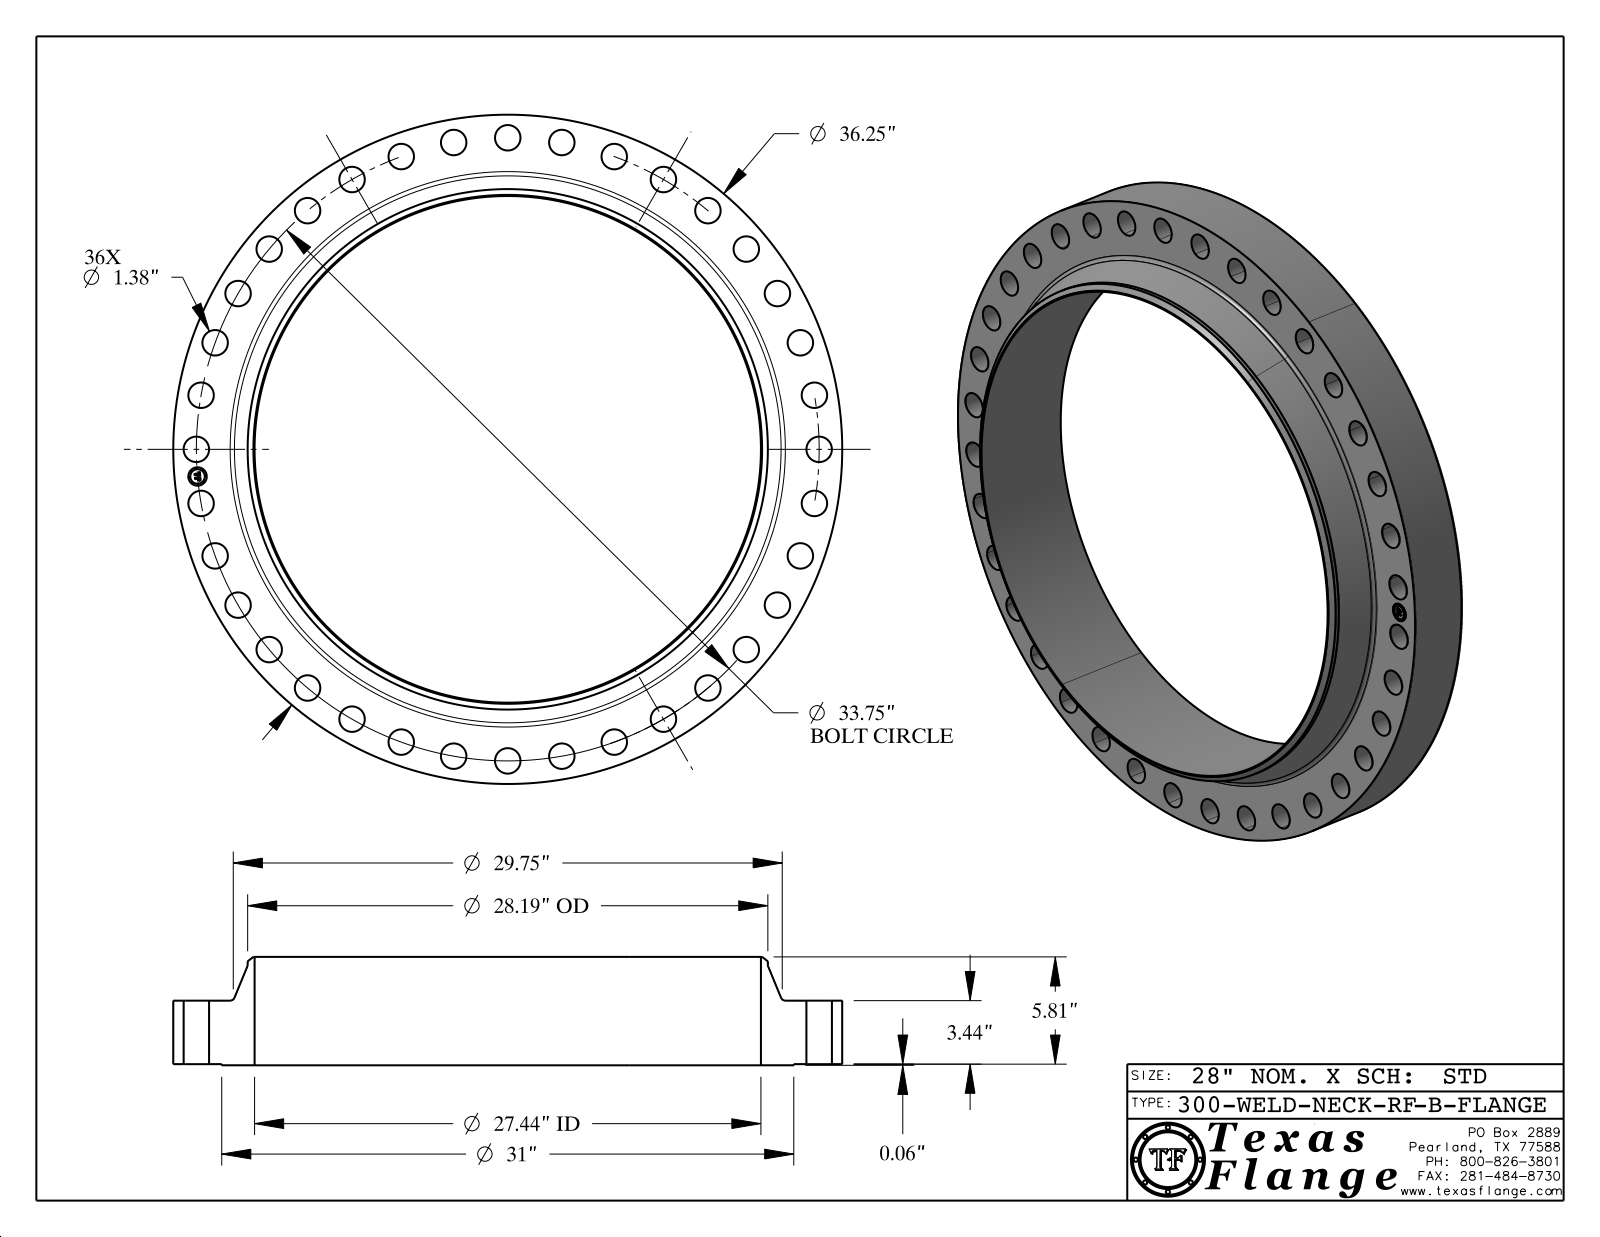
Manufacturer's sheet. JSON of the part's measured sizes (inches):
{"part_name": "300-WELD-NECK-RF, Series B", "step_written_by": "CATIA V5 STEP AP214 (AUTOMOTIVE_DESIGN)", "units": "inches", "bodies": {"solids": 1, "faces": 475, "planar": 369, "cylindrical": 100, "other": 6}, "overall_size": [36.25, 36.25, 5.873], "volume_in3": 1483, "surface_area_in2": 2355, "round_holes": [[1.38, 36], [1, 1], [27.44, 1]], "round_bosses_or_shafts": [[0.061, 8], [36.25, 1], [31, 1], [28.19, 1], [0.788, 1]], "face_to_face_distances": [3.44, 0.063, 3.503, 5.873, 5.81, 2.37, 0.015, 3.488, 3.425, 2.385], "hole_center_spacings": [16.875, 33.622, 32.6, 16.875, 23.865, 2.941, 21.694, 25.854]}
